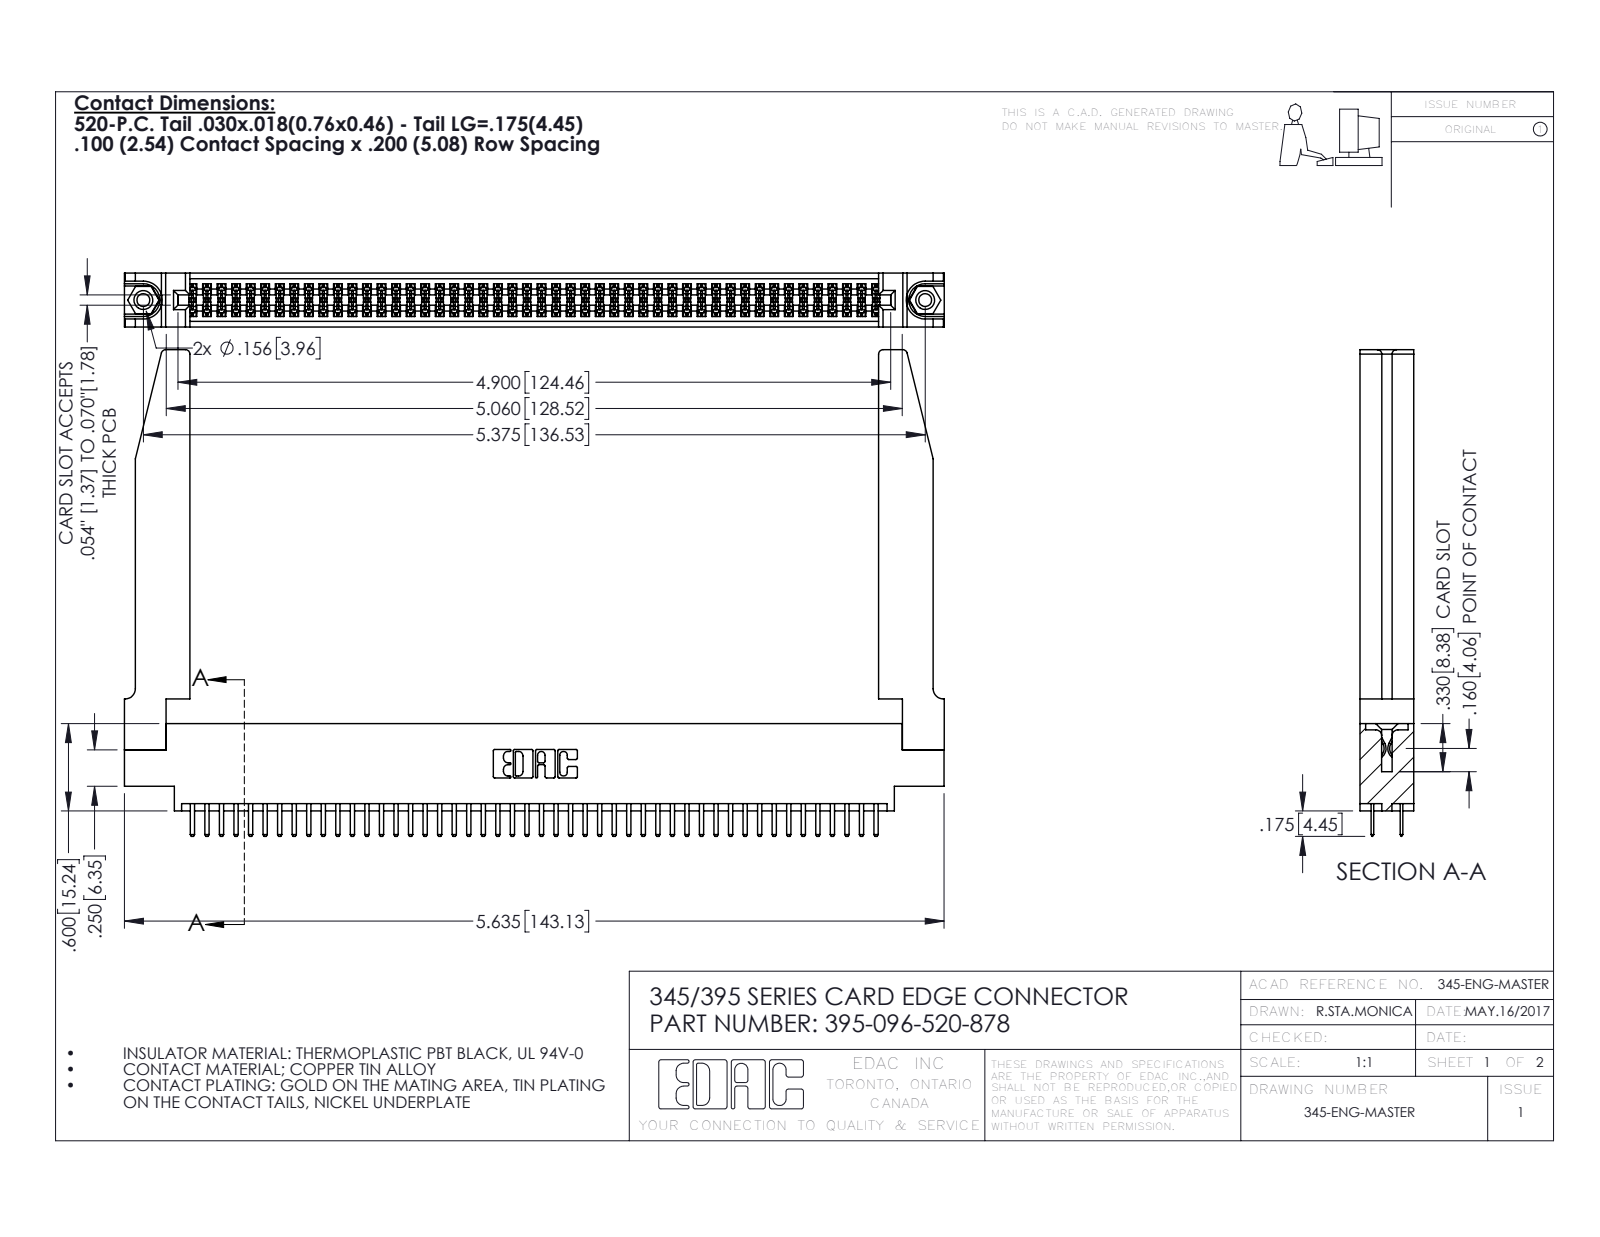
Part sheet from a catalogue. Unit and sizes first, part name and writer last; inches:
Units: inches
Overall size (bounding box): 5.636 × 3.345 × 0.37
Round holes (diameter × count): ⌀0.089 ×2, ⌀0.125 ×2, ⌀0.156 ×2, ⌀0.064 ×1
Round bosses / shafts (diameter × count): ⌀0.155 ×2
Partial cylindrical surfaces — rounded edges, fillets, slot ends (radius × count): R0.006 ×145, R0.01 ×100, R0.01 ×22, R0.03 ×8, R0.007 ×6, R0.031 ×6, R0.026 ×3, R0.014 ×2
Main face-to-face distances: 0.37, 0.072, 0.298, 0.2, 0.098, 0.272, 0.025, 0.225, 0.022, 0.072
Hole centre spacings: 0.27, 5.139, 5.375
Volume: 1.317 in³ · Surface area: 42.5 in²
Bodies: 101 solids, 5548 faces (3586 planar, 1910 cylindrical, 52 other)
Part name (STEP PRODUCT): 345-250-001_345-250-001-102; 345-220-078_345-220-078; 345 Part_0.170 Offset - 0.156 Dia-TH; 345-292-001_345-293-120 (+1 more)
STEP written by: SolidWorks 2016 (CONFIG_CONTROL_DESIGN)
